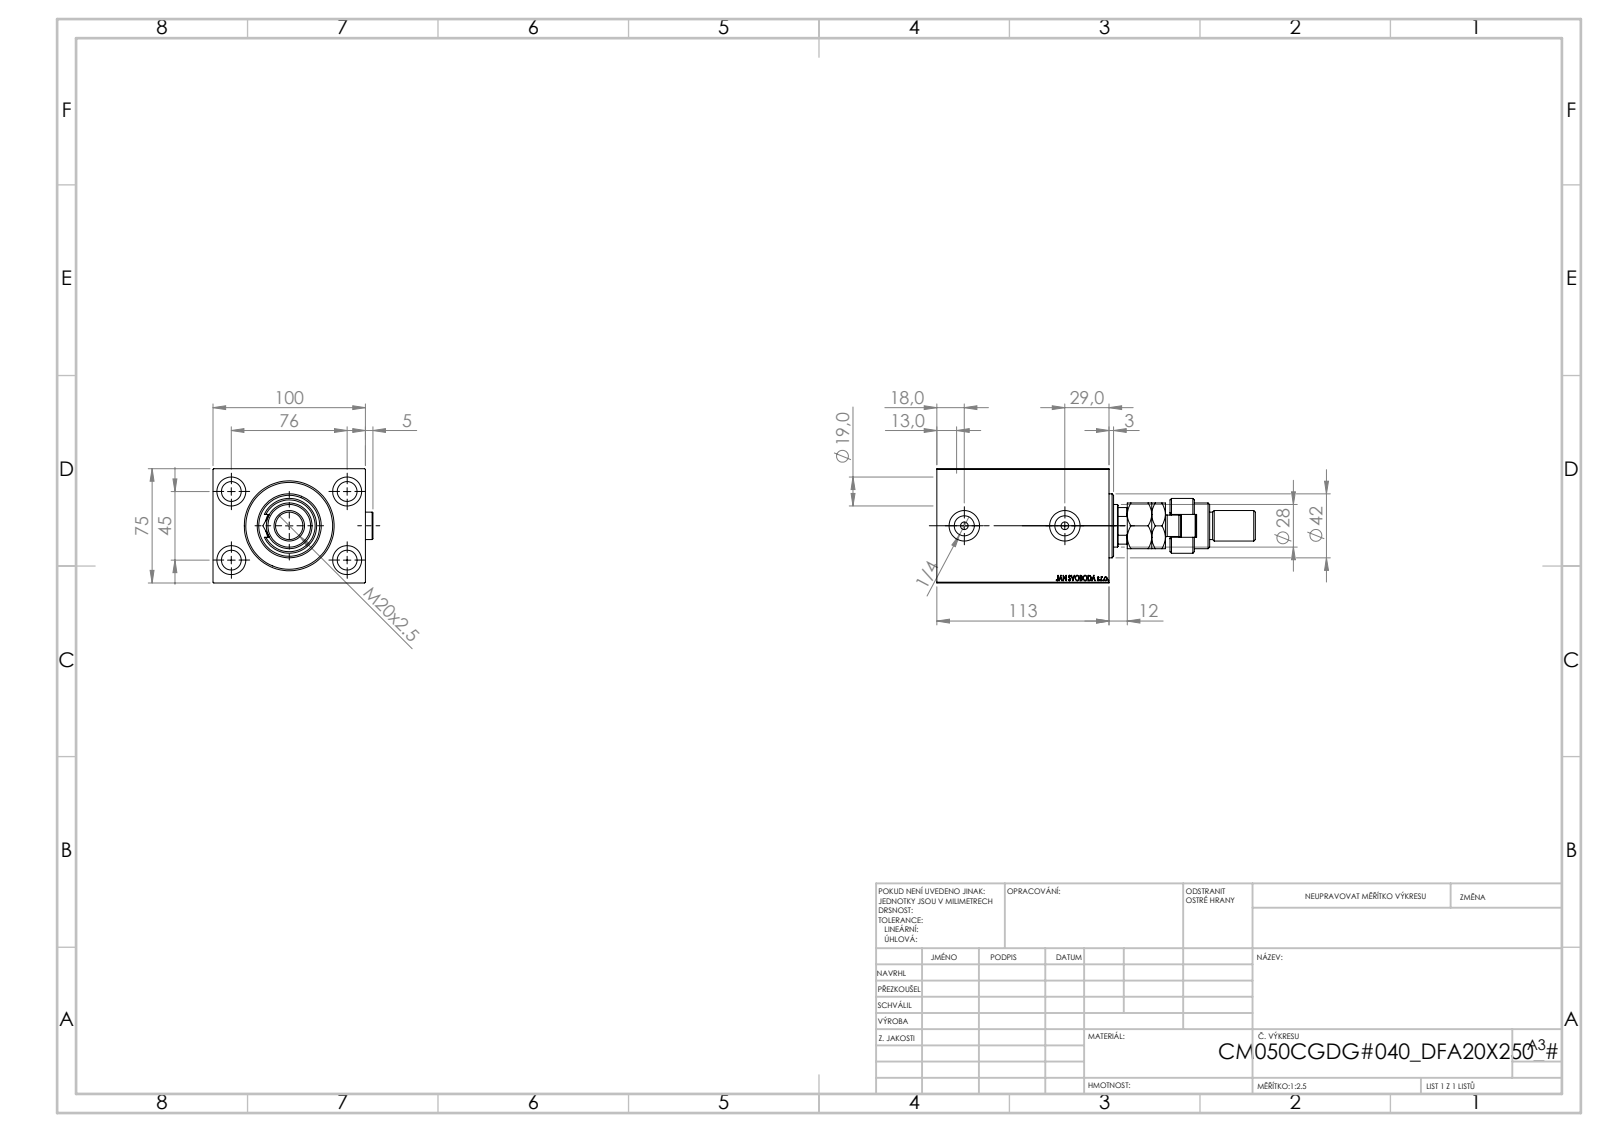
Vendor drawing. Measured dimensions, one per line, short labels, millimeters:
name: V450CM_C_Body; Zatka_OIL_PORT; MFA; FEMALE_PART_FOR_DFA (+2 more)
written by: SolidWorks 2019 (CONFIG_CONTROL_DESIGN)
unit: mm
bodies: 7 solids, 1004 faces (471 planar, 91 cylindrical, 442 other)
size: 209 × 104.9 × 75
volume: 762 445 mm³; area: 133 134 mm²
holes: 4× ⌀13, 4× ⌀19, 2× ⌀5, 2× ⌀13.16, 2× ⌀20, 1× ⌀18.5, 1× ⌀28, 1× ⌀31.5, 1× ⌀50, 1× ⌀52, 1× ⌀57
bosses: 3× ⌀18, 1× ⌀42, 1× ⌀36, 1× ⌀30, 1× ⌀22, 1× ⌀20, 1× ⌀14
rounds: 1× R7.5, 1× R12, 1× R13.5
face distances: 75, 100, 113, 99, 14, 12, 87, 47, 52, 40
hole spacings: 44.16, 45, 76, 88.32, 66
